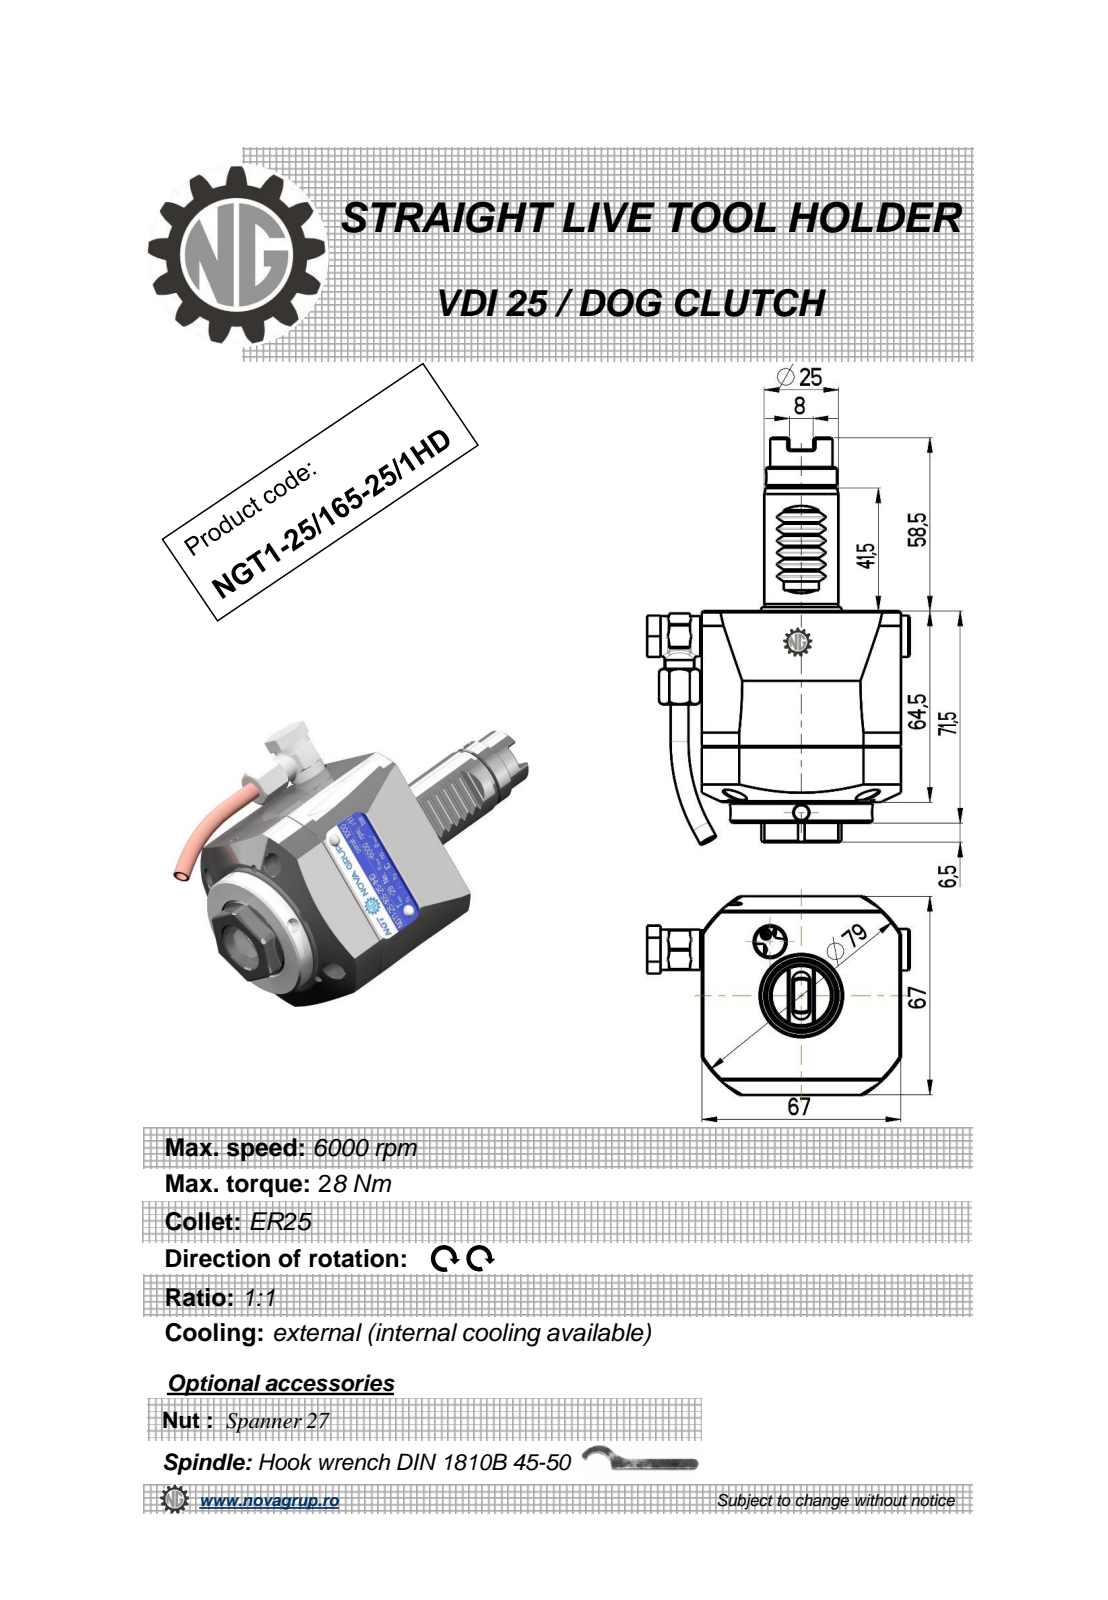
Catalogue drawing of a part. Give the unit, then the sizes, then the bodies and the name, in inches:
Units: inches
Overall size (bounding box): 5.407 × 3.48 × 2.638
Round holes (diameter × count): ⌀0.157 ×3, ⌀0.197 ×2, ⌀0.008 ×1, ⌀0.118 ×1, ⌀0.165 ×1, ⌀0.244 ×1, ⌀0.354 ×1, ⌀0.394 ×1, ⌀0.433 ×1, ⌀0.709 ×1, ⌀1.043 ×1
Round bosses / shafts (diameter × count): ⌀0.236 ×2, ⌀1.89 ×1, ⌀0.984 ×1, ⌀0.945 ×1, ⌀0.827 ×1, ⌀0.742 ×1, ⌀0.551 ×1, ⌀0.535 ×1
Partial cylindrical surfaces — rounded edges, fillets, slot ends (radius × count): R0.012 ×6, R0.02 ×6, R0.303 ×1, R0.315 ×1, R0.591 ×1, R1.555 ×1
Main face-to-face distances: 2.638, 0.276, 2.815, 2.539, 0.256, 0.472, 0.531, 3.071, 0.111, 1.063
Hole centre spacings: 0.016, 1.726, 1.741, 2.202, 2.421, 4.459
Volume: 18.46 in³ · Surface area: 55.19 in²
Bodies: 1 solid, 361 faces (126 planar, 103 cylindrical, 132 other)
Part name (STEP PRODUCT): NGT1_25_165_25_1HD
STEP written by: PRO/ENGINEER BY PARAMETRIC TECHNOLOGY CORPORATION, 2010280 (CONFIG_CONTROL_DESIGN)
